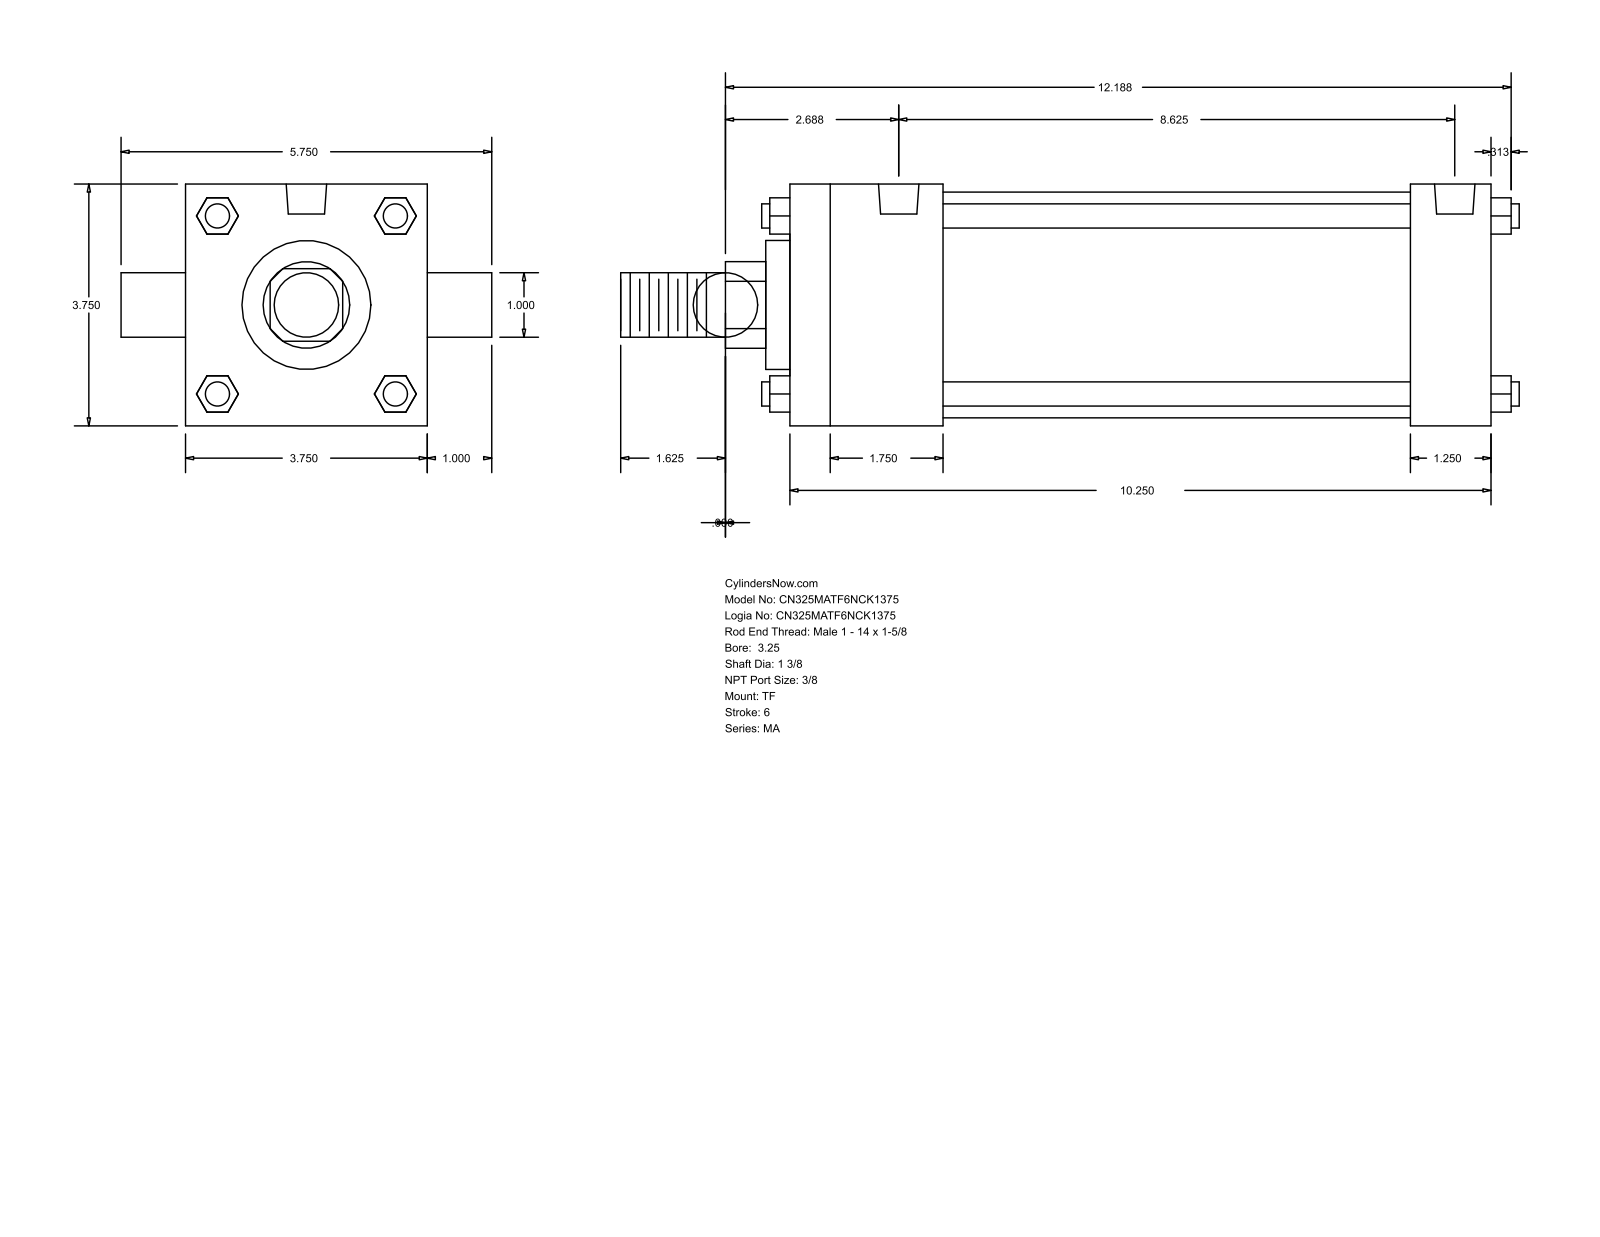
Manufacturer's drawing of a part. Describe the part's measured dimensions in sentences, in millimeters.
The part is named "MA_TF__0325_1.375". Its 3-D file was written by "GSSL Pune (CONFIG_CONTROL_DESIGN)". It is 0 solids with 120 faces: 92 planar, 28 cylindrical and 0 other. Overall it measures 354.01 by 146.05 by 95.25 millimeters. Round holes: 3 of diameter 11.11, 2 of diameter 15.93. Round bosses or shafts: 4 of diameter 9.53, 2 of diameter 25.4, 1 of diameter 88.9, 1 of diameter 50.8, 1 of diameter 34.92. Partial cylindrical surfaces (rounded edges, fillets, slot ends): 1 of radius 17.06. The main face-to-face distances are 95.24, 276.22, 60.32, 244.48, 184.16, 215.9, 31.74, 9.52, 69.84, 254. The hole center spacings are 4.77, 214.31, 209.54, 219.08.
